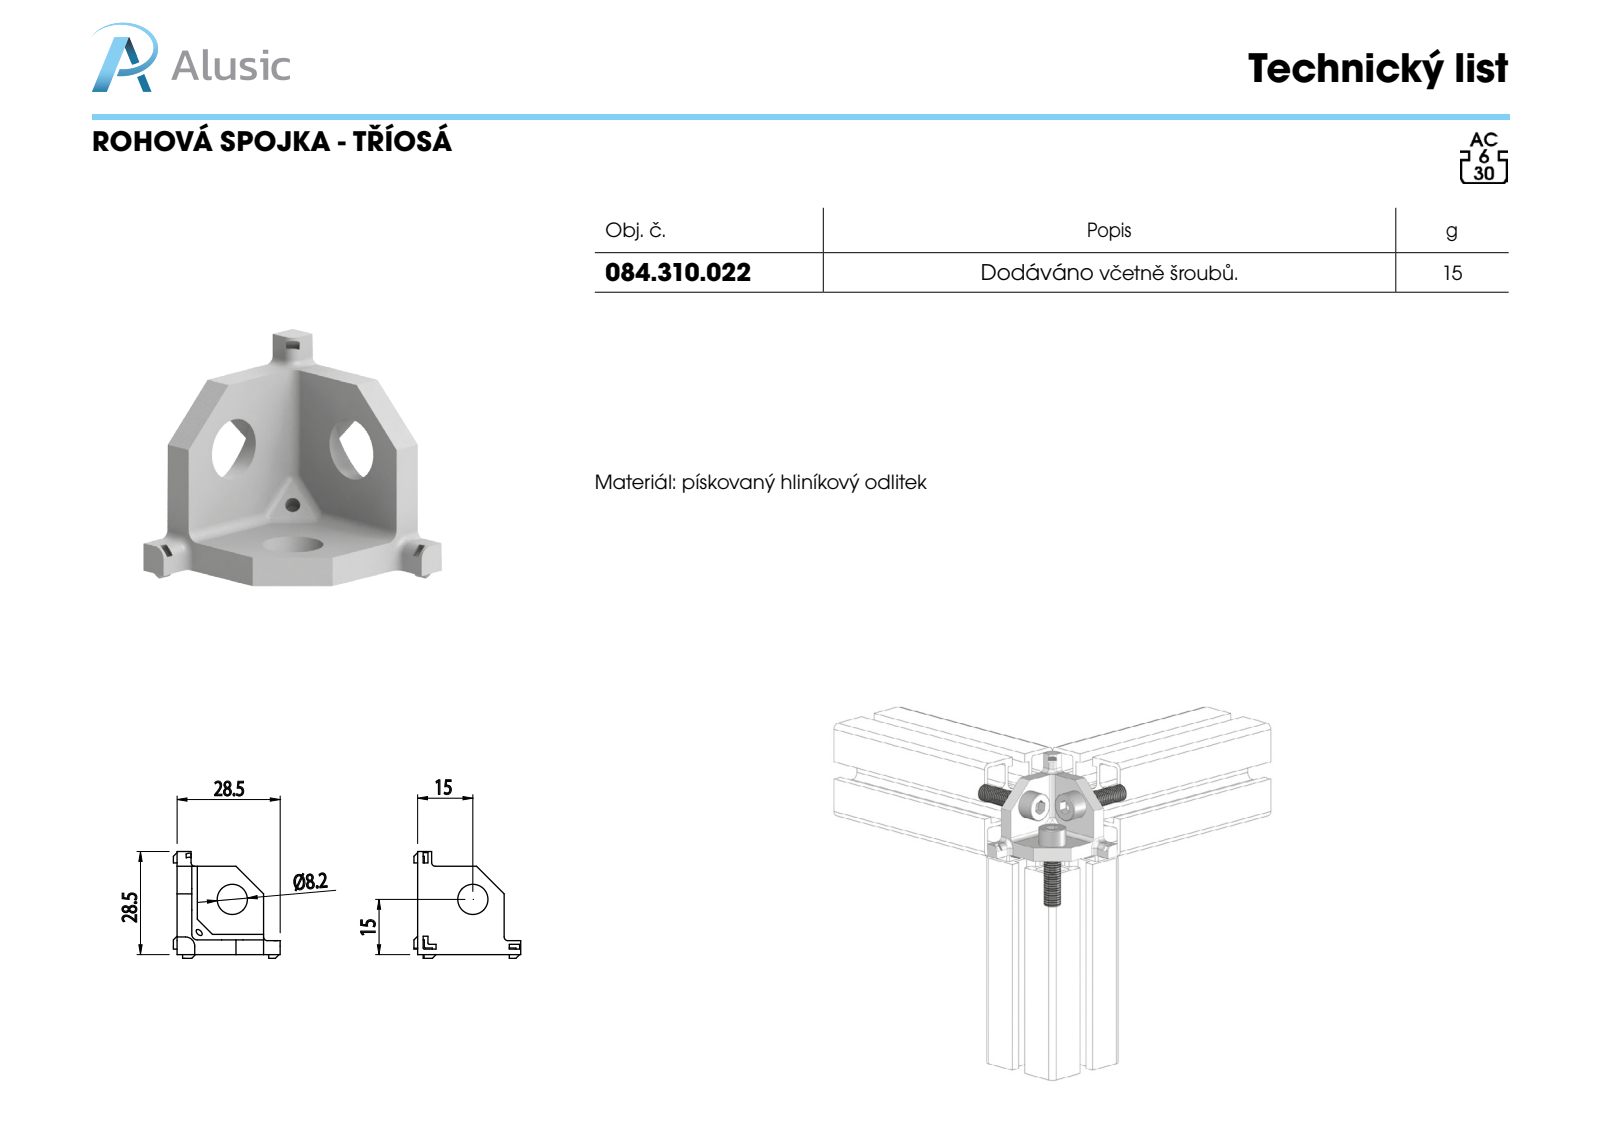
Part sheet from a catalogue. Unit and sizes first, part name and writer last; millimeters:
Units: millimetres
Overall size (bounding box): 29 × 29 × 29
Round holes (diameter × count): ⌀8.2 ×3, ⌀2 ×1
Partial cylindrical surfaces — rounded edges, fillets, slot ends (radius × count): R1.5 ×9, R1 ×6, R0.5 ×3
Main face-to-face distances: 4, 23.5, 19.5, 24, 20, 3.8, 28, 24.2, 2.5, 2.12
Volume: 4 870 mm³ · Surface area: 3 356 mm²
Bodies: 1 solid, 149 faces (106 planar, 35 cylindrical, 8 other)
Part name (STEP PRODUCT): 084.310.022
STEP written by: SolidWorks 2012 (CONFIG_CONTROL_DESIGN)
